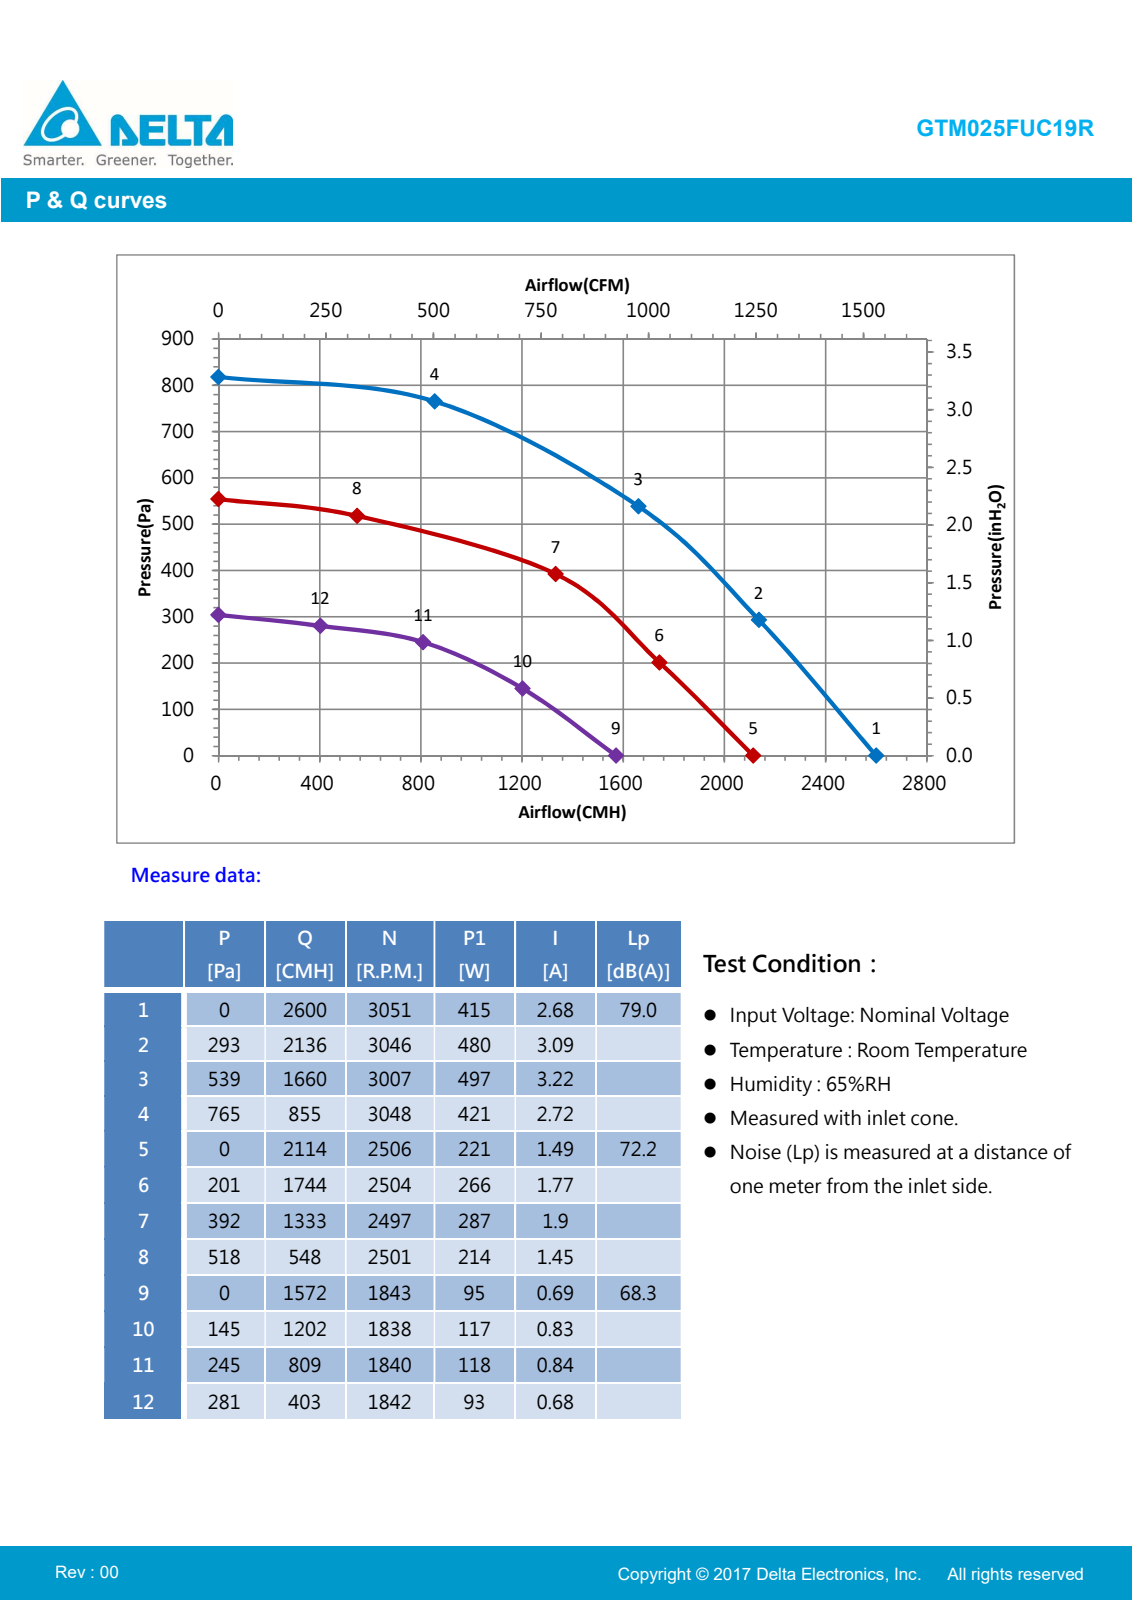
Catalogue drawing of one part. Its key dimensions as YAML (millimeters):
part_name: "TOP-PLATE; SUPPORT-2; SUPPORT-22R; BOTTOM-PLATE (+8 more)"
step_written_by: "PRO/ENGINEER BY PARAMETRIC TECHNOLOGY CORPORATION, 2010180 (CONFIG_CONTROL_DESIGN)"
units: millimeters
bodies: {solids: 72, faces: 4987, planar: 2052, cylindrical: 1268, other: 1667}
overall_size: [400, 400, 346.38]
volume: 1418000
surface_area: 1287000
round_holes:
  - {diameter: 6.5, count: 22}
  - {diameter: 6, count: 12}
  - {diameter: 5, count: 9}
  - {diameter: 3, count: 8}
  - {diameter: 4, count: 8}
  - {diameter: 4.5, count: 8}
  - {diameter: 5.6, count: 6}
  - {diameter: 2.3, count: 4}
  - {diameter: 2.5, count: 4}
  - {diameter: 11, count: 4}
  - {diameter: 2.8, count: 3}
  - {diameter: 4.7, count: 3}
round_bosses_or_shafts:
  - {diameter: 12, count: 16}
  - {diameter: 11, count: 12}
  - {diameter: 10, count: 8}
  - {diameter: 8, count: 8}
  - {diameter: 6, count: 4}
  - {diameter: 14.5, count: 2}
  - {diameter: 9, count: 2}
  - {diameter: 255, count: 1}
partial_cylinders:
  - {radius: 0.2, count: 161}
  - {radius: 1, count: 139}
  - {radius: 0.5, count: 138}
  - {radius: 0.6, count: 120}
  - {radius: 2, count: 28}
  - {radius: 0.33, count: 24}
  - {radius: 0.4, count: 24}
  - {radius: 0.84, count: 24}
face_to_face_distances: [2, 182.5, 155.8, 26.7, 180.5, 184.5, 153.8, 282, 157.8, 24.7]
hole_center_spacings: [59.32, 62.76, 68.95, 82, 84.9, 97.16, 131.2, 137.3]
